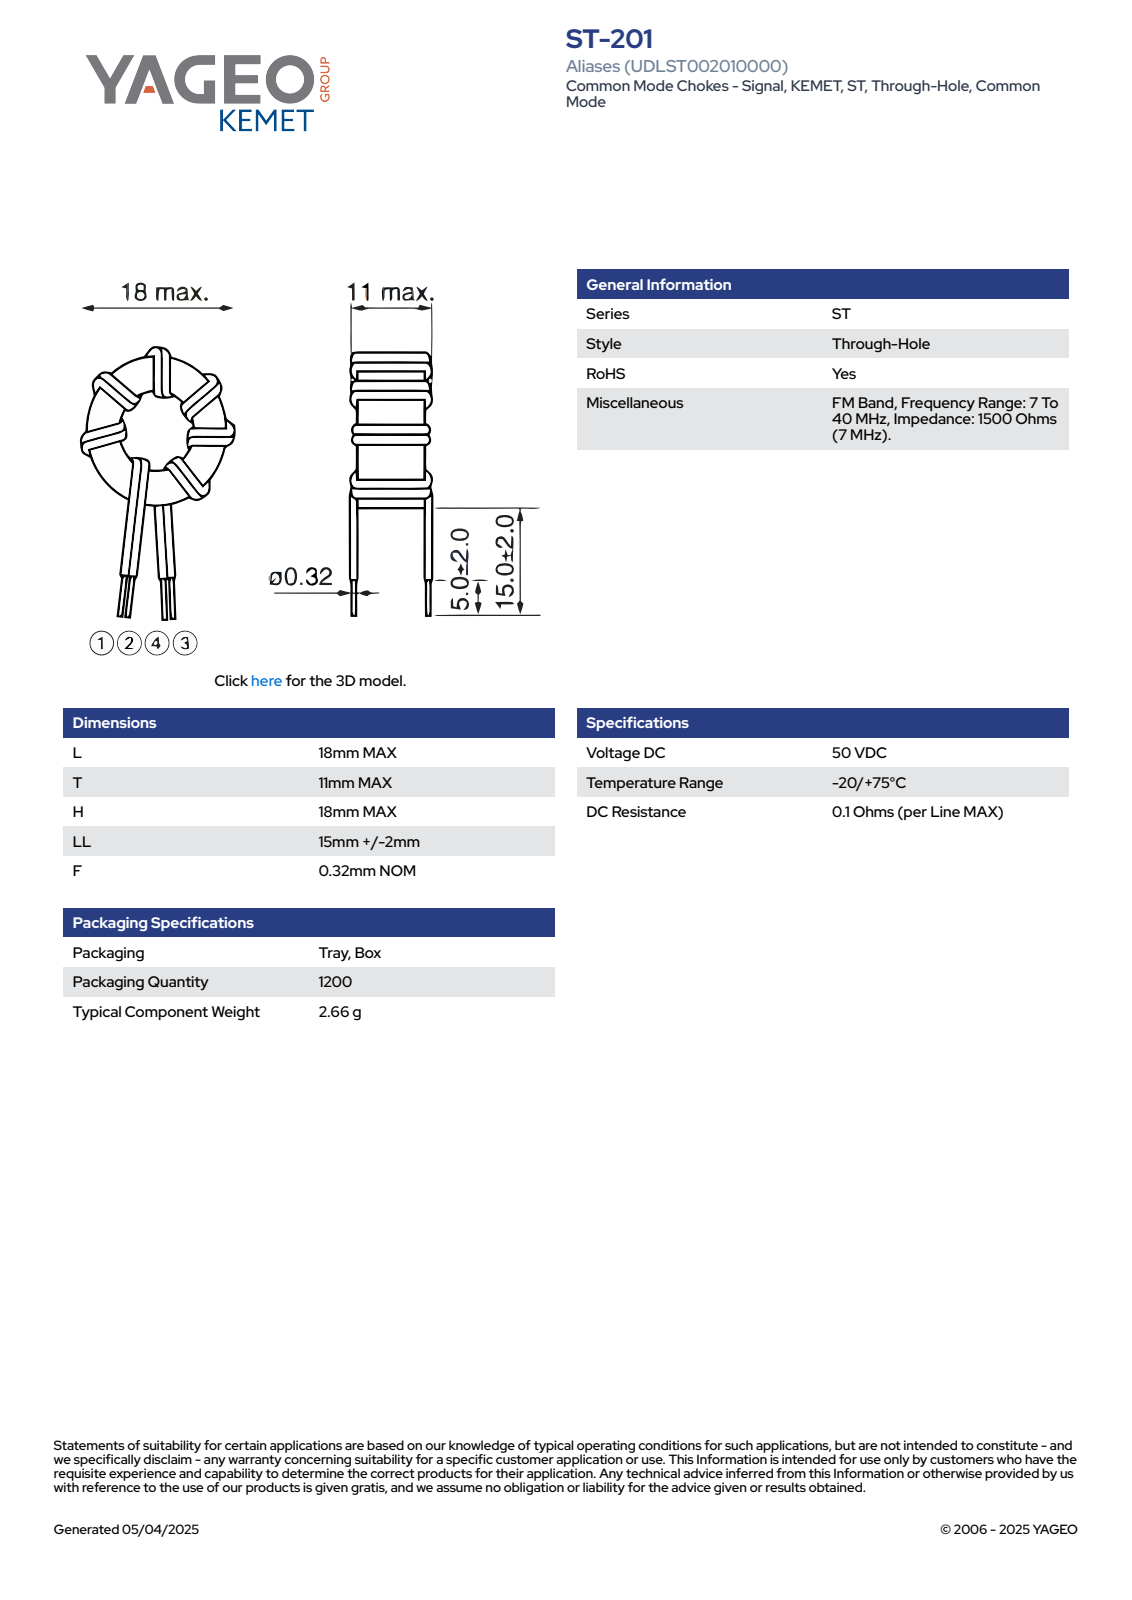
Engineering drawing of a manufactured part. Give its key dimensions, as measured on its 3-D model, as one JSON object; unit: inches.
{"part_name": "IFC_NTST101_L18T11H18", "step_written_by": "SolidWorks 2014 (AUTOMOTIVE_DESIGN)", "units": "inches", "bodies": {"solids": 17, "faces": 410, "planar": 10, "cylindrical": 272, "other": 128}, "overall_size": [1.356, 0.709, 0.433], "volume_in3": 0.142, "surface_area_in2": 3.173, "round_holes": [[0.071, 1]], "round_bosses_or_shafts": [[0.02, 40], [0.02, 4], [0.013, 4], [0.665, 1]], "partial_cylinders_radius": [[0.01, 16]], "face_to_face_distances": [0.39, 0.276]}
